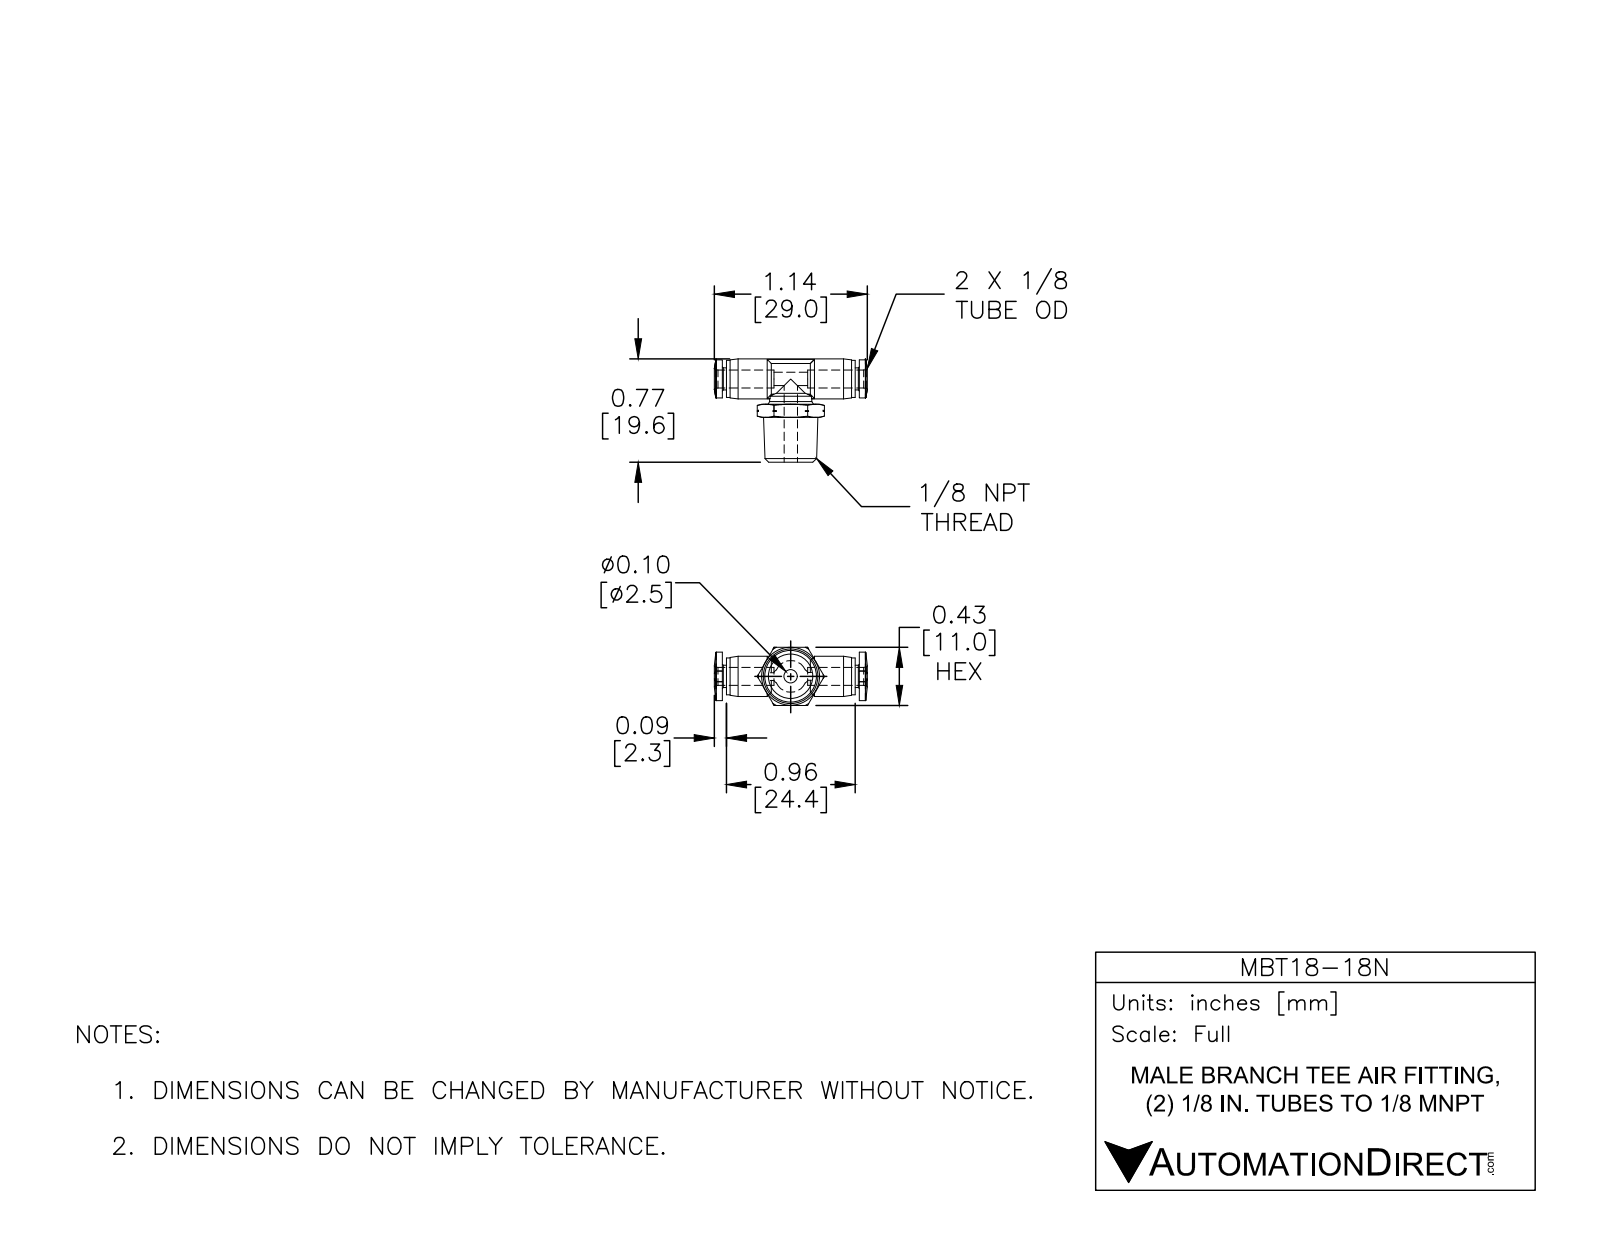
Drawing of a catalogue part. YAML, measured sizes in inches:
part_name: "MBT18-18N"
step_written_by: "SolidWorks 2015 (CONFIG_CONTROL_DESIGN)"
units: inches
bodies: {solids: 1, faces: 146, planar: 29, cylindrical: 34, other: 83}
overall_size: [1.142, 0.772, 0.433]
volume: 0.113
surface_area: 2.797
round_holes:
  - {diameter: 0.098, count: 2}
  - {diameter: 0.134, count: 1}
round_bosses_or_shafts:
  - {diameter: 0.315, count: 1}
  - {diameter: 0.299, count: 1}
  - {diameter: 0.276, count: 1}
  - {diameter: 0.236, count: 1}
  - {diameter: 0.165, count: 1}
partial_cylinders:
  - {radius: 0.142, count: 2}
  - {radius: 0.118, count: 1}
face_to_face_distances: [0.433, 0.031, 0.992, 1.024, 0.961, 0.187, 0.246, 0.059, 0.335, 0.098]
